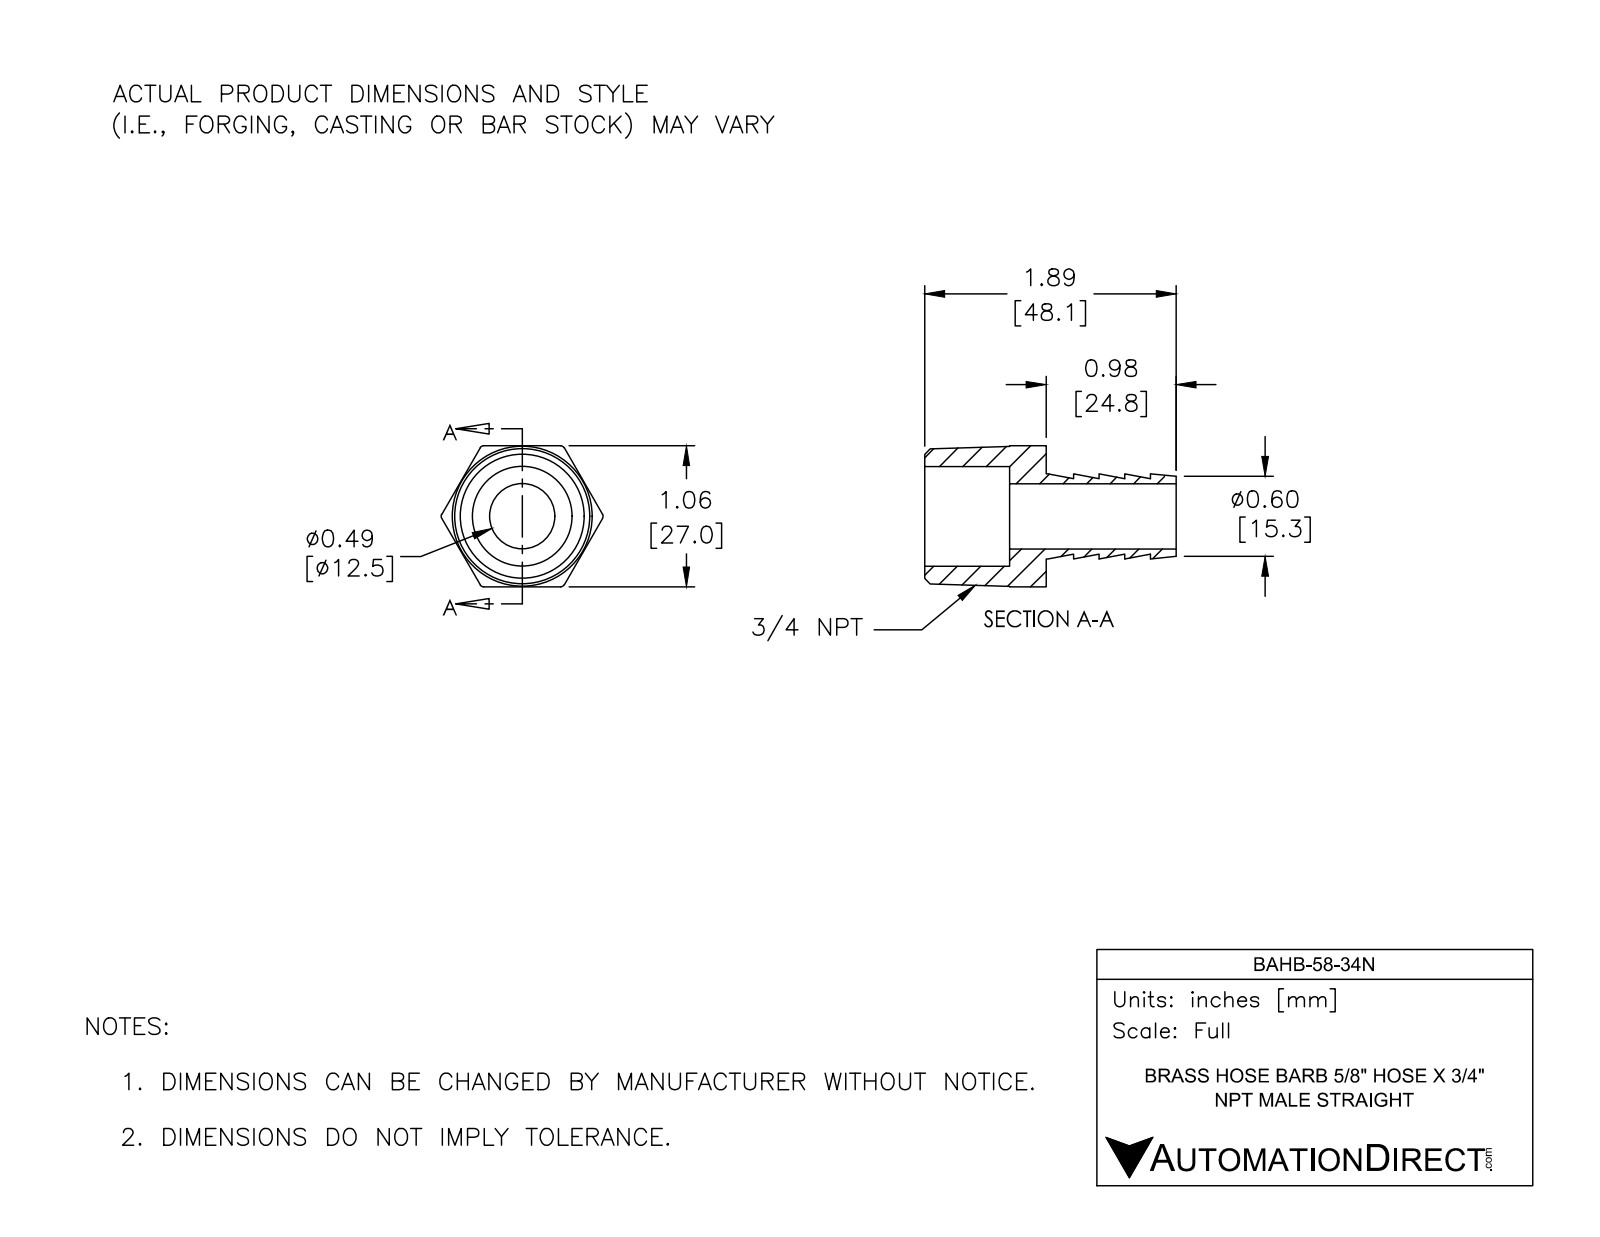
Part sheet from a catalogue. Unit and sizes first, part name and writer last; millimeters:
Units: millimetres
Overall size (bounding box): 48.1 × 30.9 × 27
Round holes (diameter × count): ⌀12.5 ×1, ⌀19.1 ×1
Round bosses / shafts (diameter × count): ⌀16.3 ×1
Partial cylindrical surfaces — rounded edges, fillets, slot ends (radius × count): R0.8 ×6
Main face-to-face distances: 27, 7, 23.2, 16.3, 4.9, 9.8, 14.7, 19.9, 26.9, 43.2
Volume: 9 230 mm³ · Surface area: 6 484 mm²
Bodies: 1 solid, 41 faces (15 planar, 12 cylindrical, 14 other)
Part name (STEP PRODUCT): BAHB-58-34N
STEP written by: SolidWorks 2017 (AUTOMOTIVE_DESIGN)
